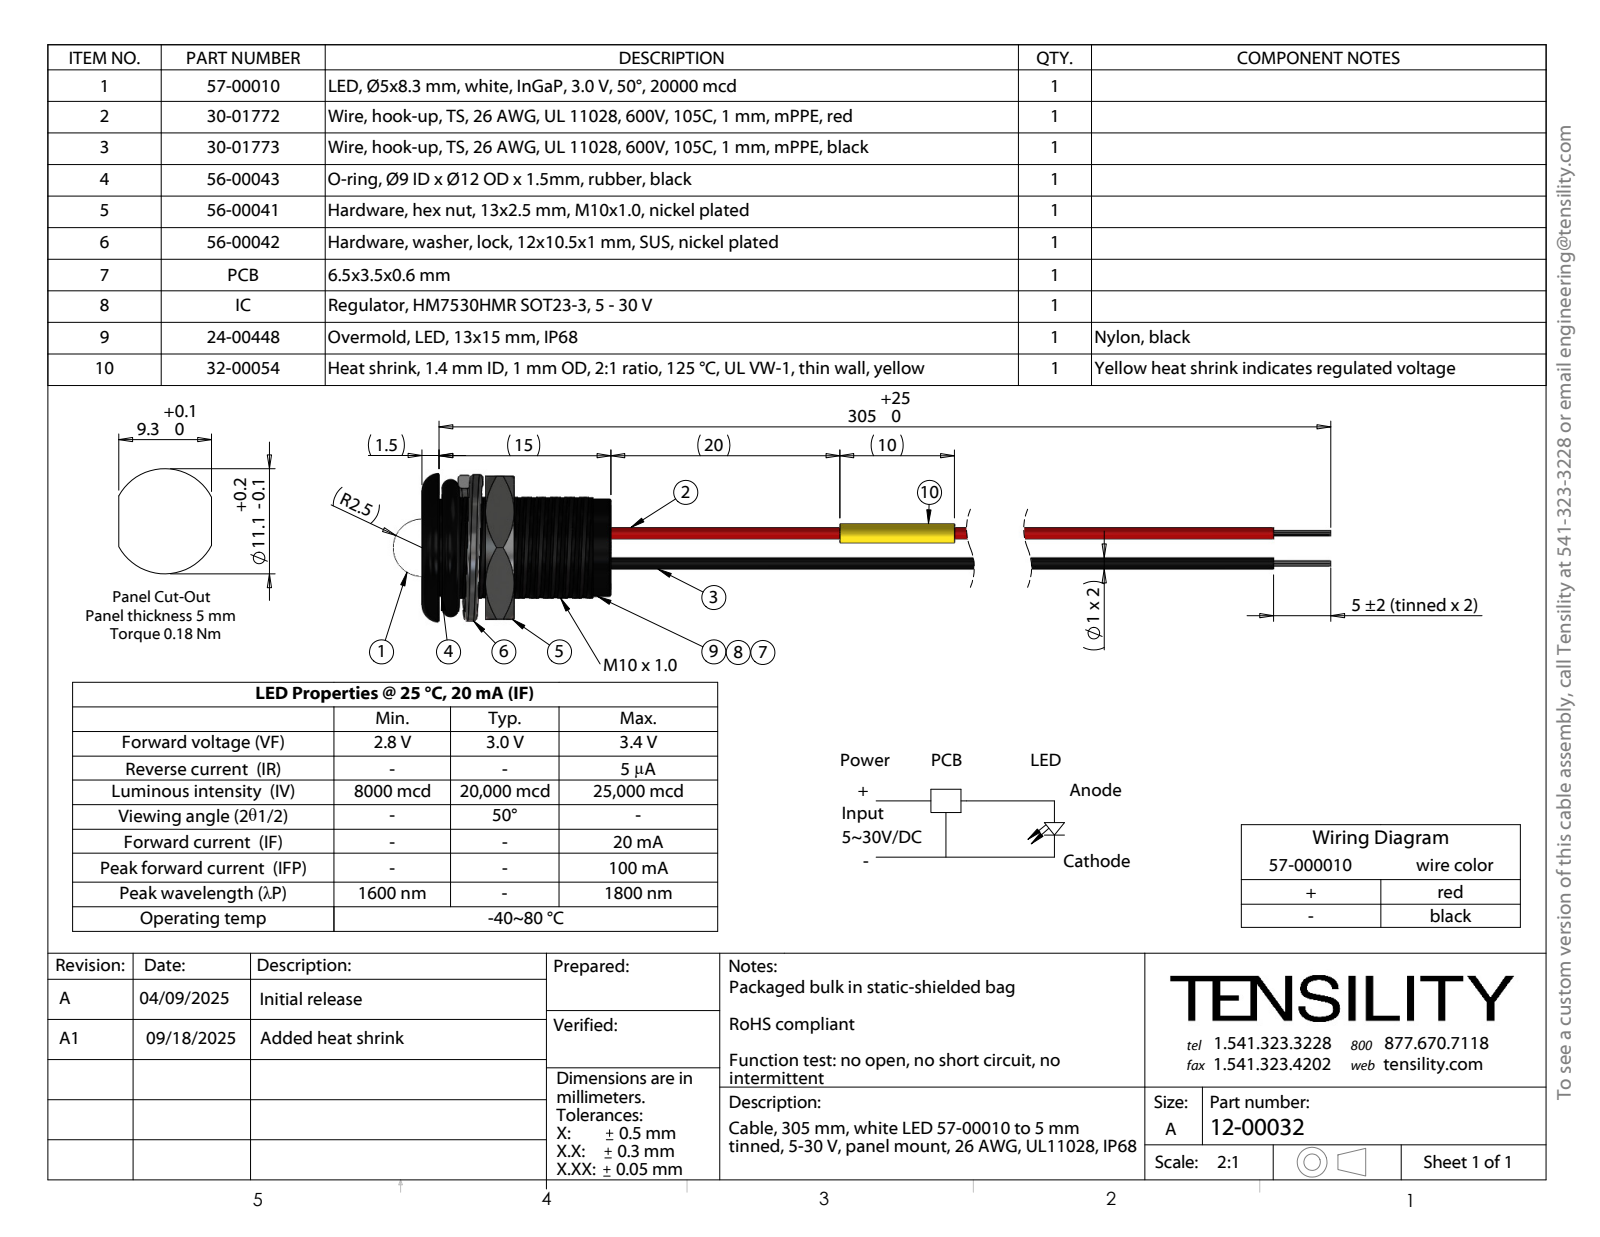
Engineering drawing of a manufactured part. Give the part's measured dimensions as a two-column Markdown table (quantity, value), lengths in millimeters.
| quantity | value |
| --- | --- |
| part name | 56-00042_Split washer; 56-00043; 12-00032; 30-01773_stripped and tinned (+4 more) |
| STEP written by | SolidWorks 2021 (CONFIG_CONTROL_DESIGN) |
| units | millimeters |
| bodies | 57 solids, 514 faces (185 planar, 246 cylindrical, 83 other) |
| overall size | 173.99 × 14.43 × 12.99 |
| volume | 1 769 mm³ |
| surface area | 6 568 mm² |
| round holes (diameter × count) | 1 × 2 |
| round bosses / shafts (diameter × count) | 1 × 2, 0.83 × 2, 8.5 × 1, 5 × 1 |
| partial cylindrical surfaces (radius × count) | 4.33 × 1, 5 × 1 |
| main face-to-face distances | 1.5, 16.5, 15, 12.5, 8.06, 6.56, 8.44, 5.56, 4.06, 2.5 |
| hole center spacings | 0.36, 0.38, 0.33, 2.43, 2.35, 2.48, 2.52, 2.56 |
